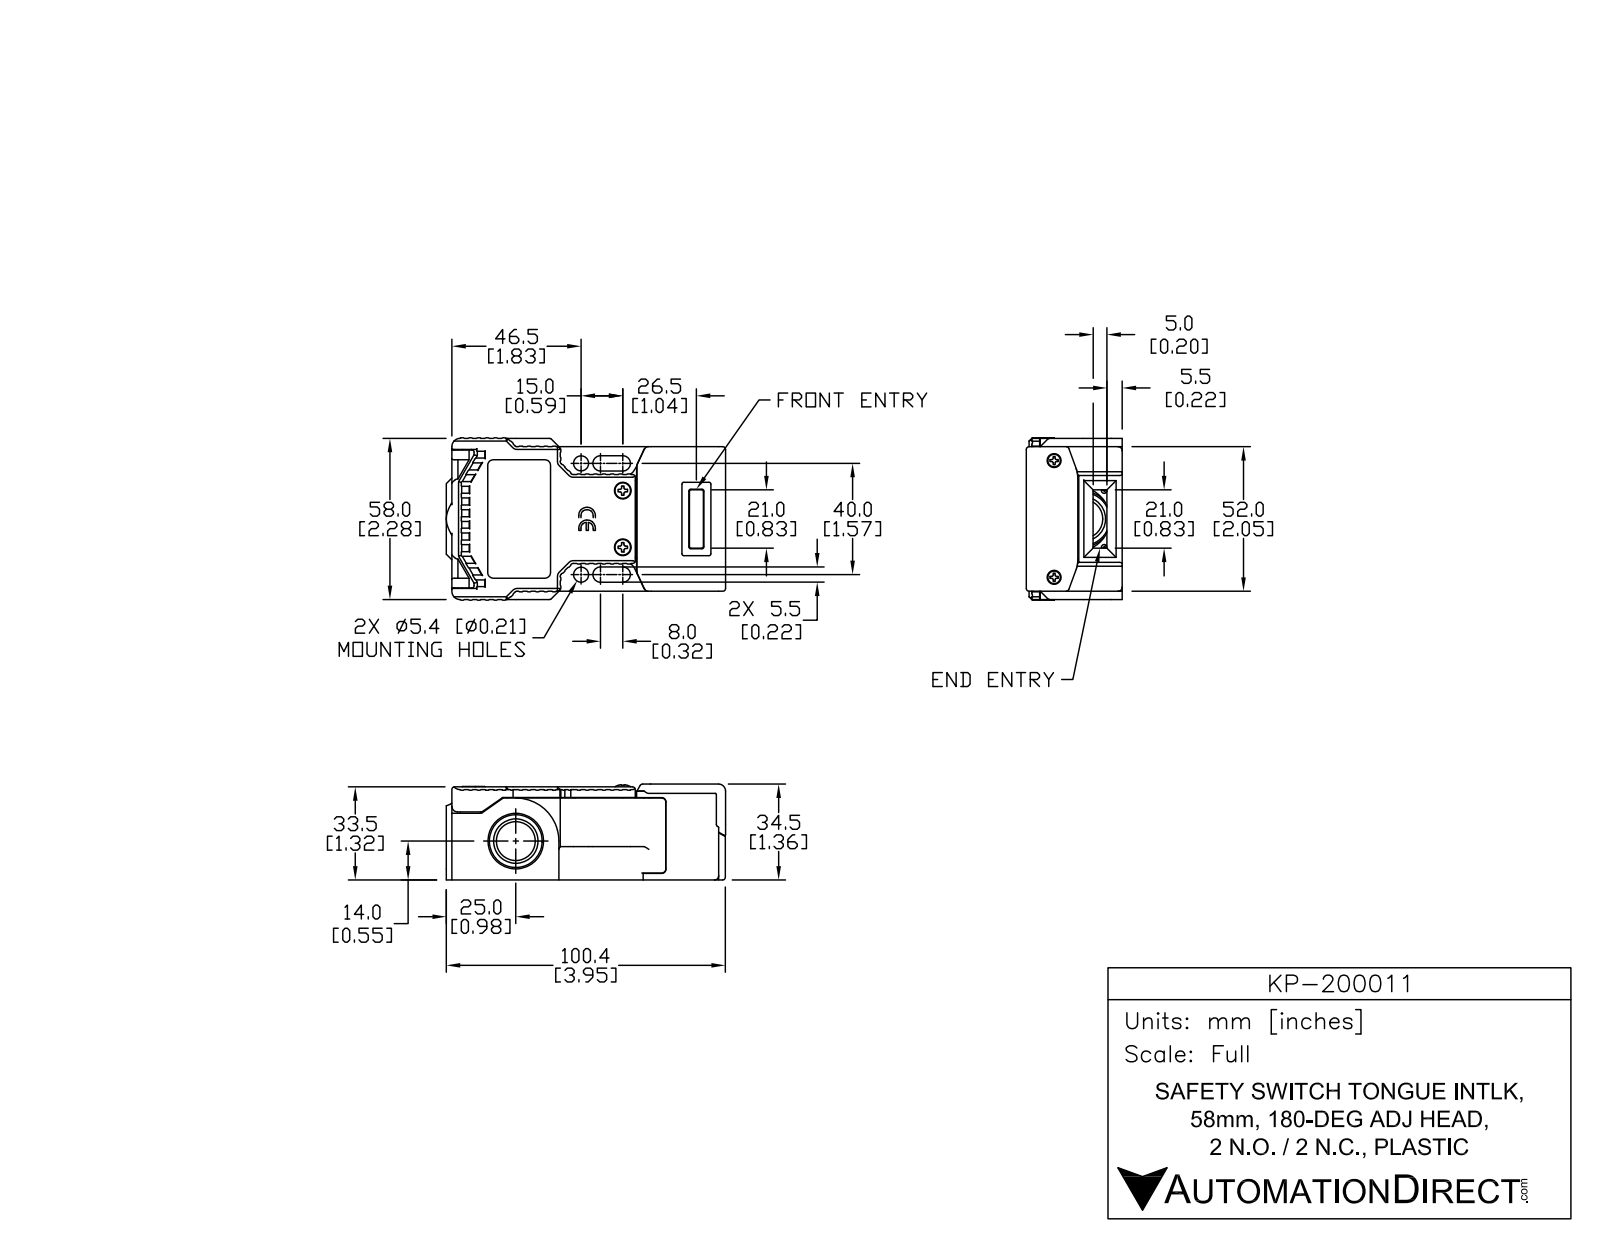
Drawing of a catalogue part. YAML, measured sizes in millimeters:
part_name: "KP-200011"
step_written_by: "SolidWorks 2013 (AUTOMOTIVE_DESIGN)"
units: millimeters
bodies: {solids: 1, faces: 206, planar: 147, cylindrical: 32, other: 27}
overall_size: [101.85, 58, 34.6]
volume: 158770
surface_area: 25501
round_holes:
  - {diameter: 5.4, count: 2}
  - {diameter: 19.33, count: 1}
  - {diameter: 20, count: 1}
round_bosses_or_shafts:
  - {diameter: 5.6, count: 2}
  - {diameter: 4.5, count: 2}
partial_cylinders:
  - {radius: 2, count: 4}
  - {radius: 2.75, count: 4}
  - {radius: 4, count: 3}
  - {radius: 5, count: 2}
face_to_face_distances: [33.5, 52, 3, 55, 34.5, 1, 33.45, 1.05, 12.8, 98.5]
hole_center_spacings: [40]
